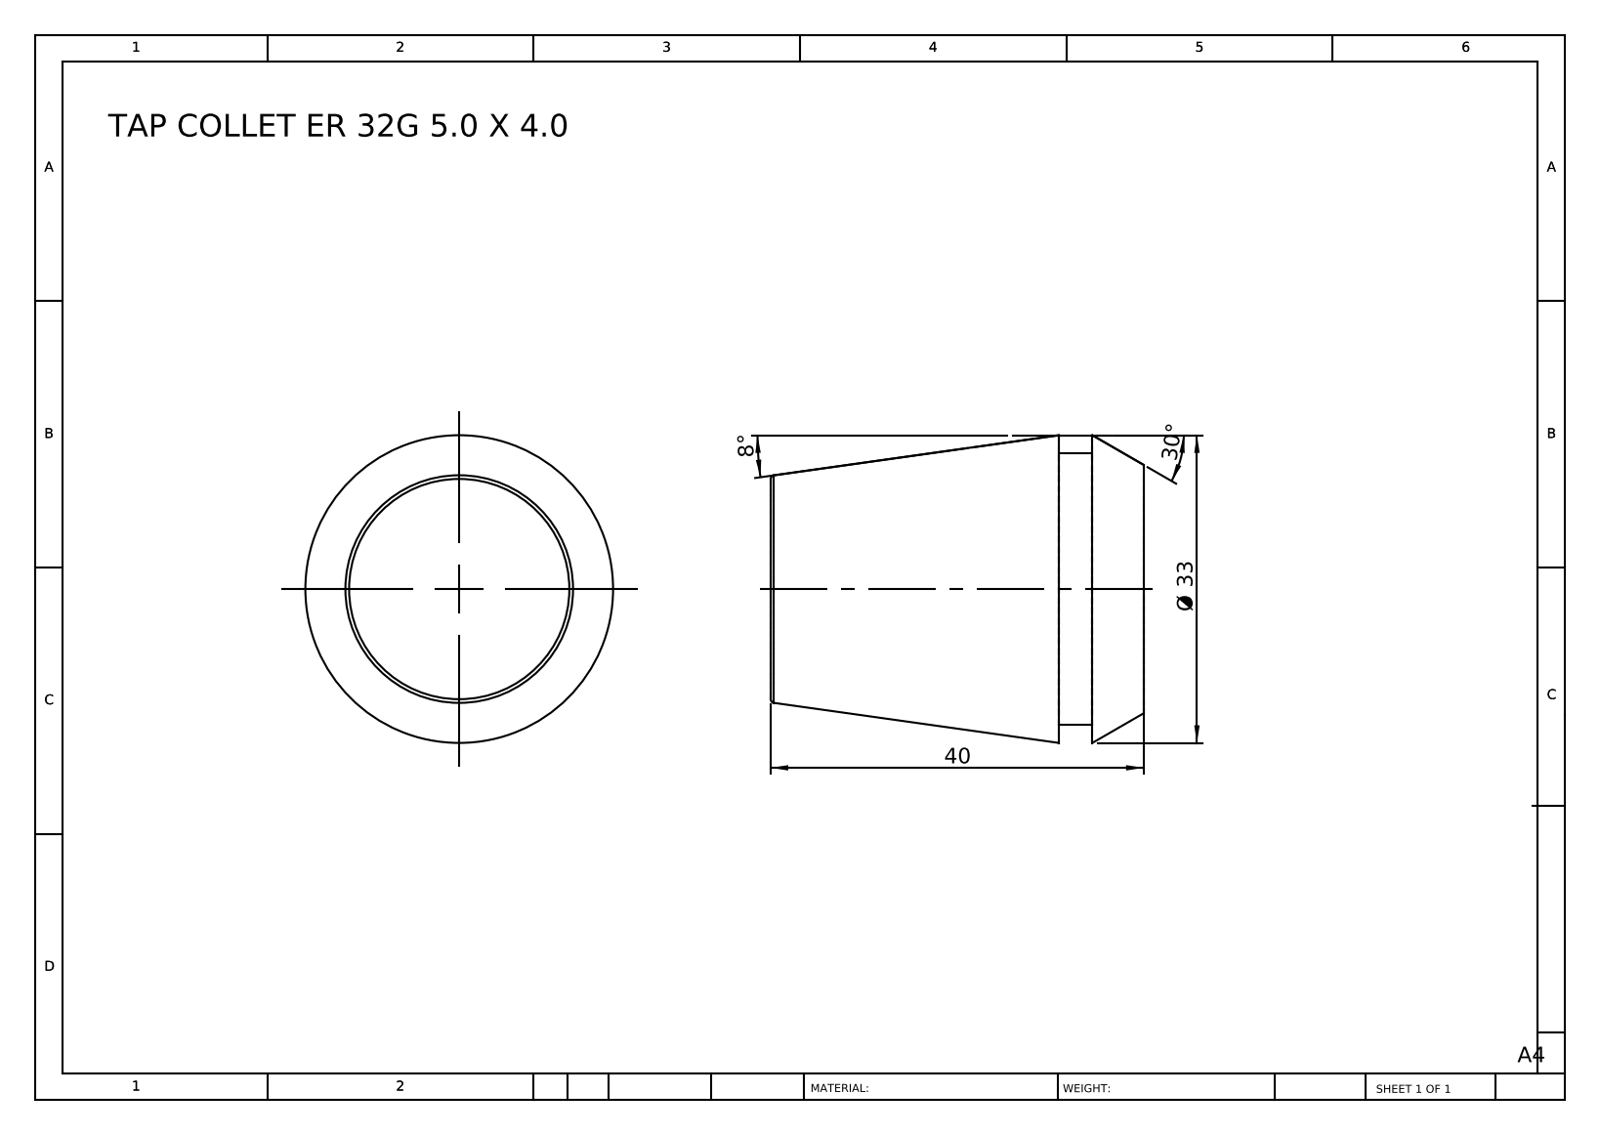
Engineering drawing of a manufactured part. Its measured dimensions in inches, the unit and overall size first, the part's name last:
Units: inches
Overall size (bounding box): 1.575 × 1.299 × 1.299
Round bosses / shafts (diameter × count): ⌀1.15 ×1
Main face-to-face distances: 1.575, 0.358, 1.217, 0.217, 0.142, 1.358
Volume: 1.608 in³ · Surface area: 7.934 in²
Bodies: 1 solid, 12 faces (4 planar, 2 cylindrical, 6 other)
Part name (STEP PRODUCT): TAP COLLET ER 32G 5.0 X 4.0
STEP written by: SolidWorks 2014 (CONFIG_CONTROL_DESIGN)
